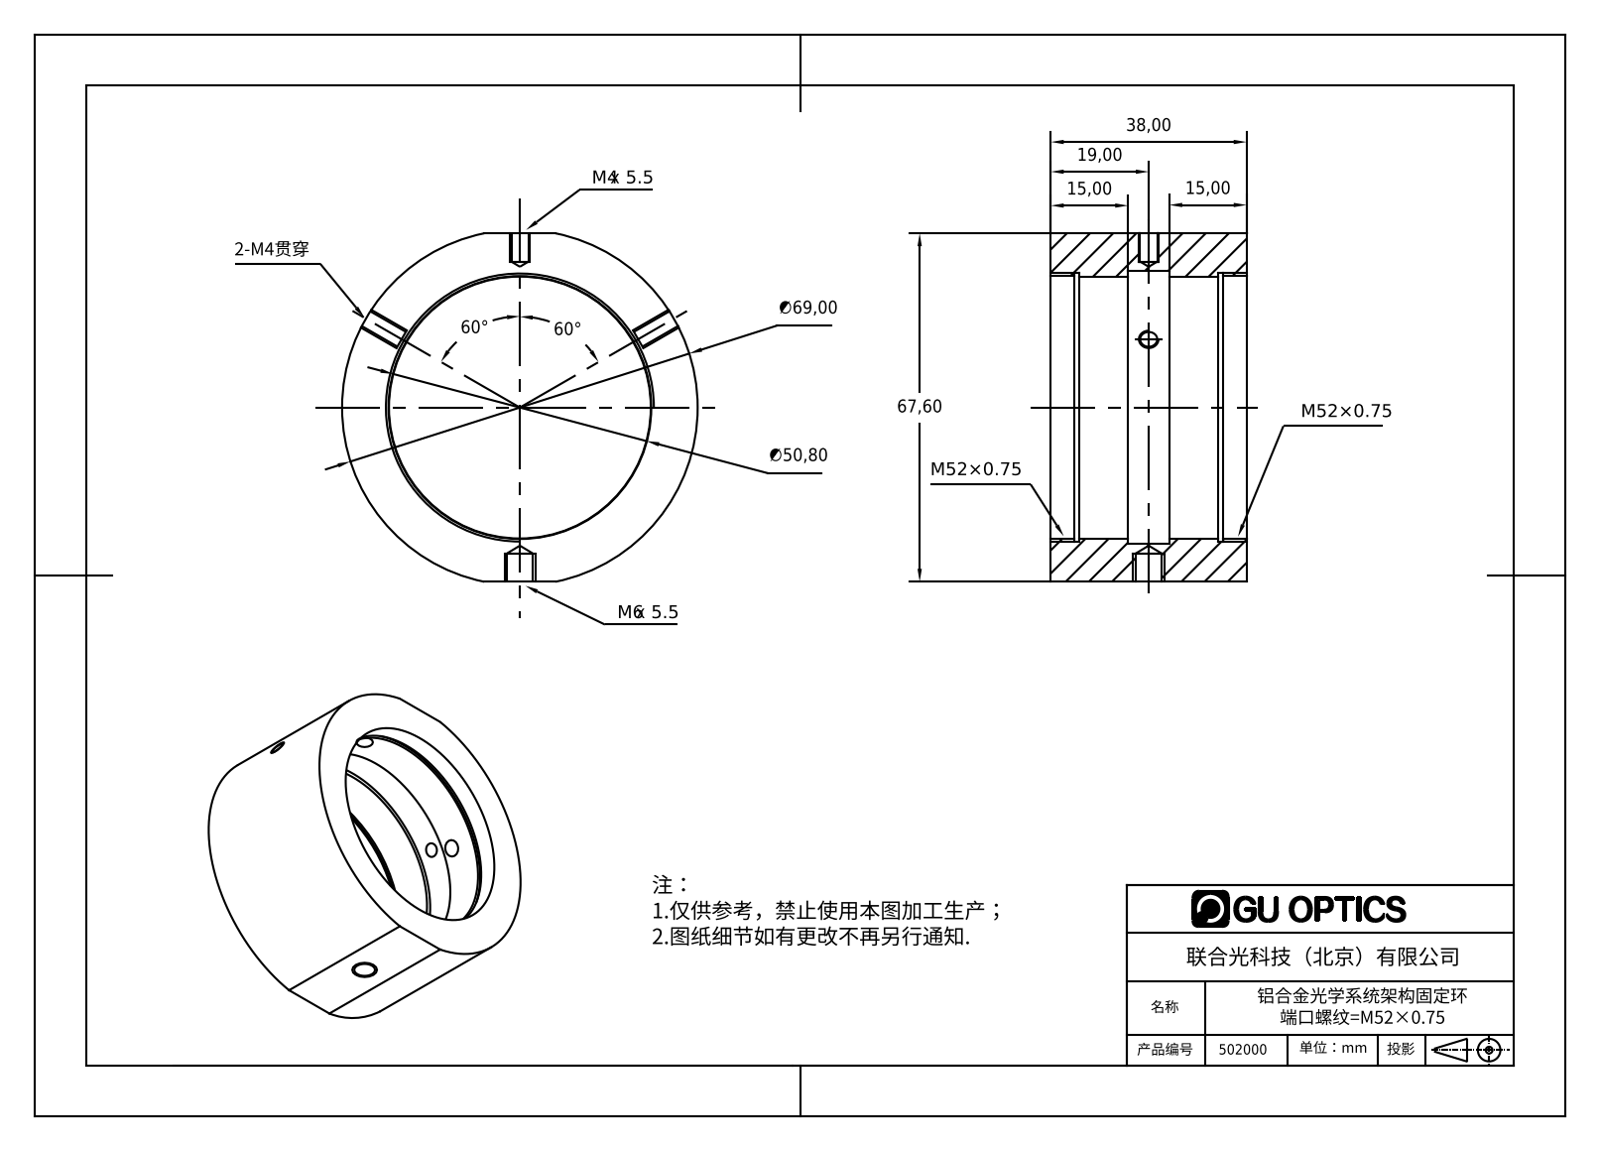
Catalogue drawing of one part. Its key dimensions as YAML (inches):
part_name: "502000"
step_written_by: "SolidWorks 2016 (CONFIG_CONTROL_DESIGN)"
units: inches
bodies: {solids: 1, faces: 39, planar: 10, cylindrical: 25, other: 4}
overall_size: [2.717, 2.661, 1.496]
volume: 3.812
surface_area: 29.13
round_holes:
  - {diameter: 0.13, count: 3}
  - {diameter: 0.197, count: 1}
  - {diameter: 2, count: 1}
  - {diameter: 2.008, count: 1}
  - {diameter: 2.055, count: 1}
  - {diameter: 2.087, count: 1}
round_bosses_or_shafts:
  - {diameter: 2.717, count: 1}
face_to_face_distances: [1.496, 2.661, 0.591, 0.906, 0.217, 1.28, 0.374, 0.689, 0.177, 1.319]
